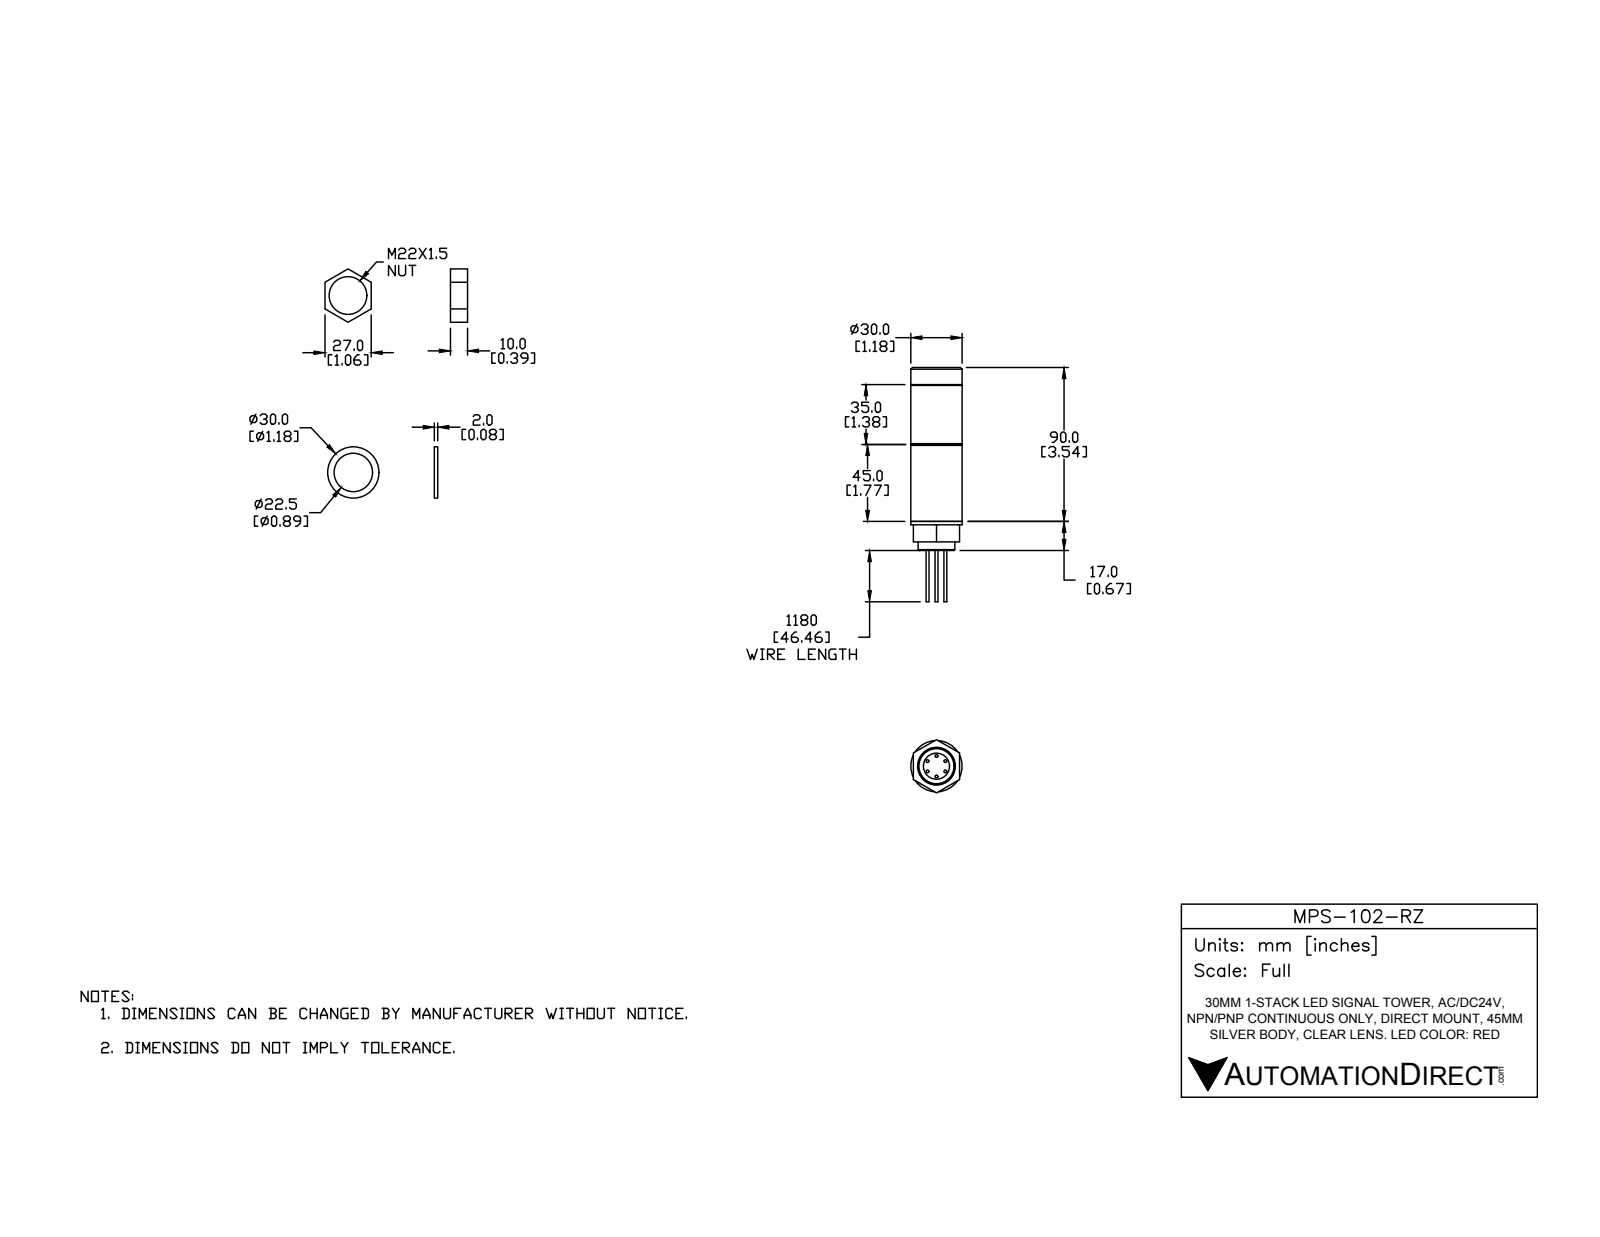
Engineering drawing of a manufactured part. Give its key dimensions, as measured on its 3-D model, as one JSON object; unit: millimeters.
{"part_name": "MPS-102-RZ", "step_written_by": "SolidWorks 2016 (AUTOMOTIVE_DESIGN)", "units": "millimeters", "bodies": {"solids": 12, "faces": 95, "planar": 47, "cylindrical": 36, "other": 12}, "overall_size": [137, 31.18, 30], "volume_mm3": 59574, "surface_area_mm2": 22895, "round_holes": [[3.2, 1], [7.7, 1], [15.3, 1], [20.7, 1], [22, 1]], "round_bosses_or_shafts": [[1.7, 6], [30, 1], [21.5, 1], [5, 1]], "face_to_face_distances": [35, 45, 47, 80, 92, 10, 12, 57, 2, 82]}
